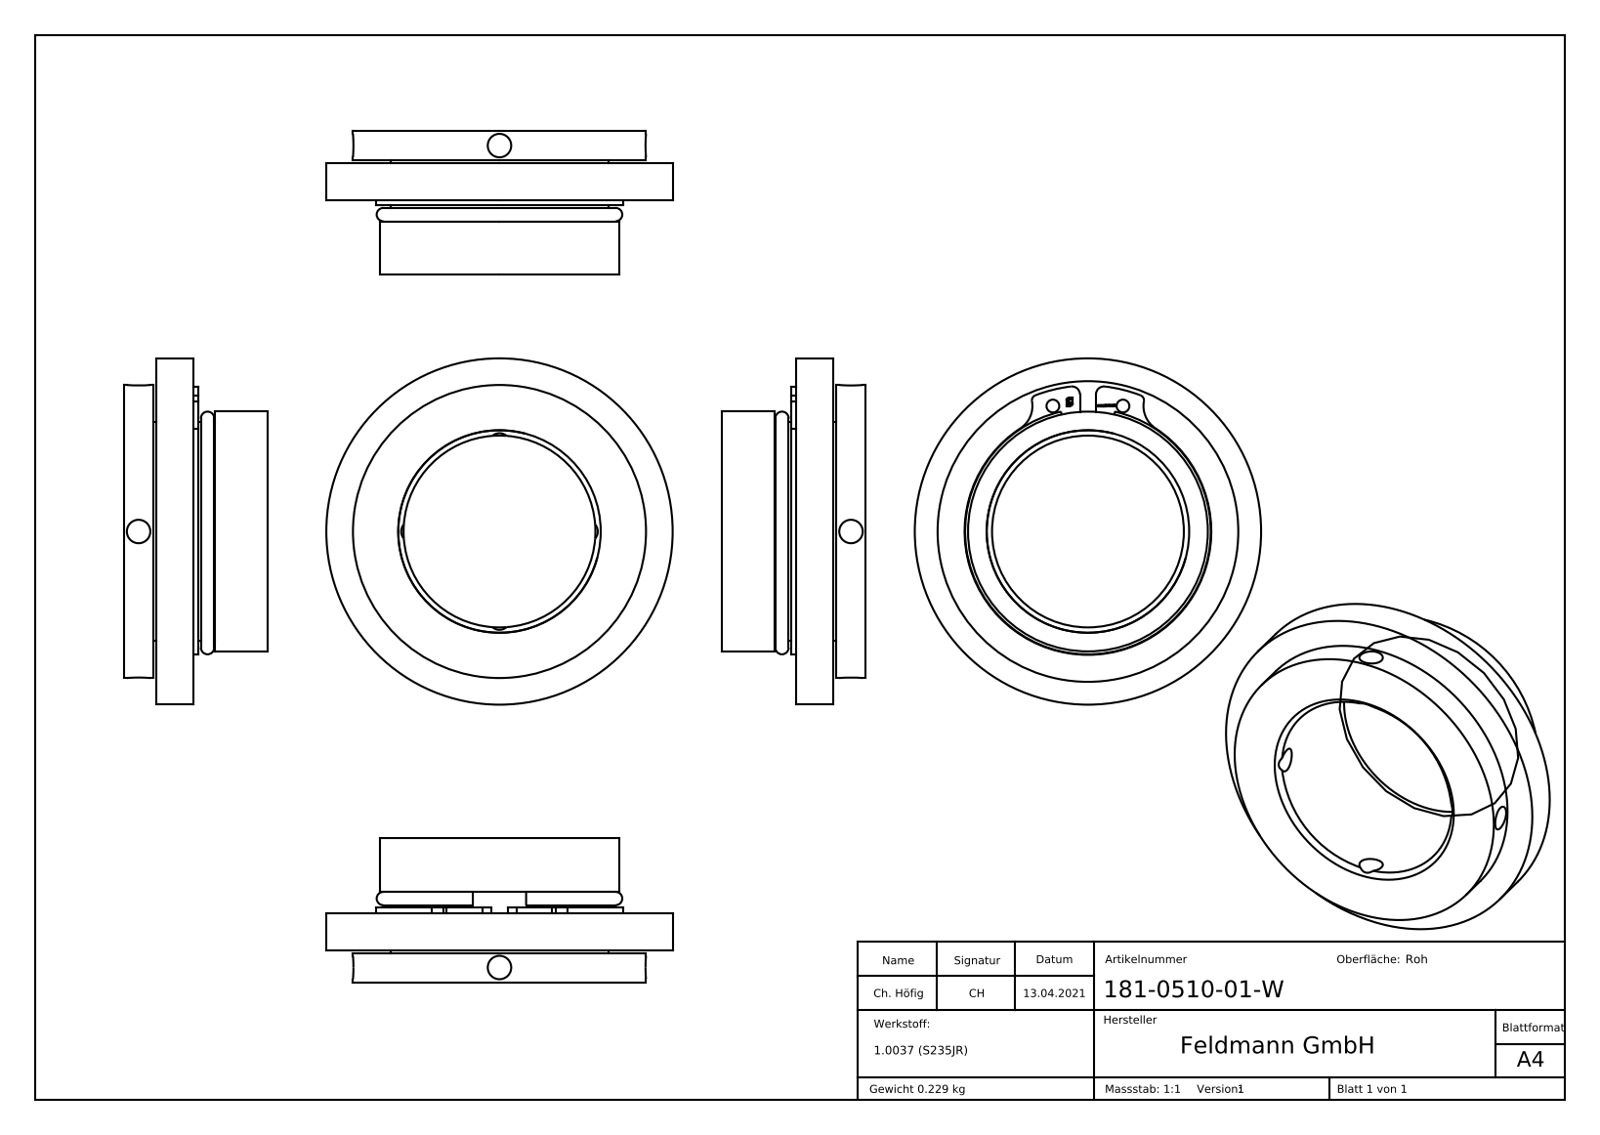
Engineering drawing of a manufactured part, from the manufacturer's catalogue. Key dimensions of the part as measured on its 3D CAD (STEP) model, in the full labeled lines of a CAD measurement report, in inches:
Part name (STEP PRODUCT): 181-0510-01-W
STEP written by: SolidWorks 2018 (CONFIG_CONTROL_DESIGN)
Units: inches
Bodies: 4 solids, 342 faces (172 planar, 42 cylindrical, 128 other)
Overall size (bounding box): 2.559 × 2.559 × 1.063
Volume: 1.792 in³ · Surface area: 29.66 in²
Round holes (diameter × count): ⌀0.094 ×2, ⌀0.173 ×2, ⌀1.417 ×1, ⌀1.618 ×1, ⌀1.654 ×1, ⌀2.222 ×1
Round bosses / shafts (diameter × count): ⌀2.559 ×1, ⌀2.165 ×1, ⌀1.823 ×1, ⌀1.772 ×1, ⌀1.614 ×1
Partial cylindrical surfaces — rounded edges, fillets, slot ends (radius × count): R0.039 ×2, R0.059 ×2, R0.197 ×2, R1.079 ×1
Main face-to-face distances: 0.24, 0.02, 0.236, 0.512, 0.22, 0.457, 0.217, 0.551, 0.055, 0.276
Hole centre spacings: 0.963, 0.518
